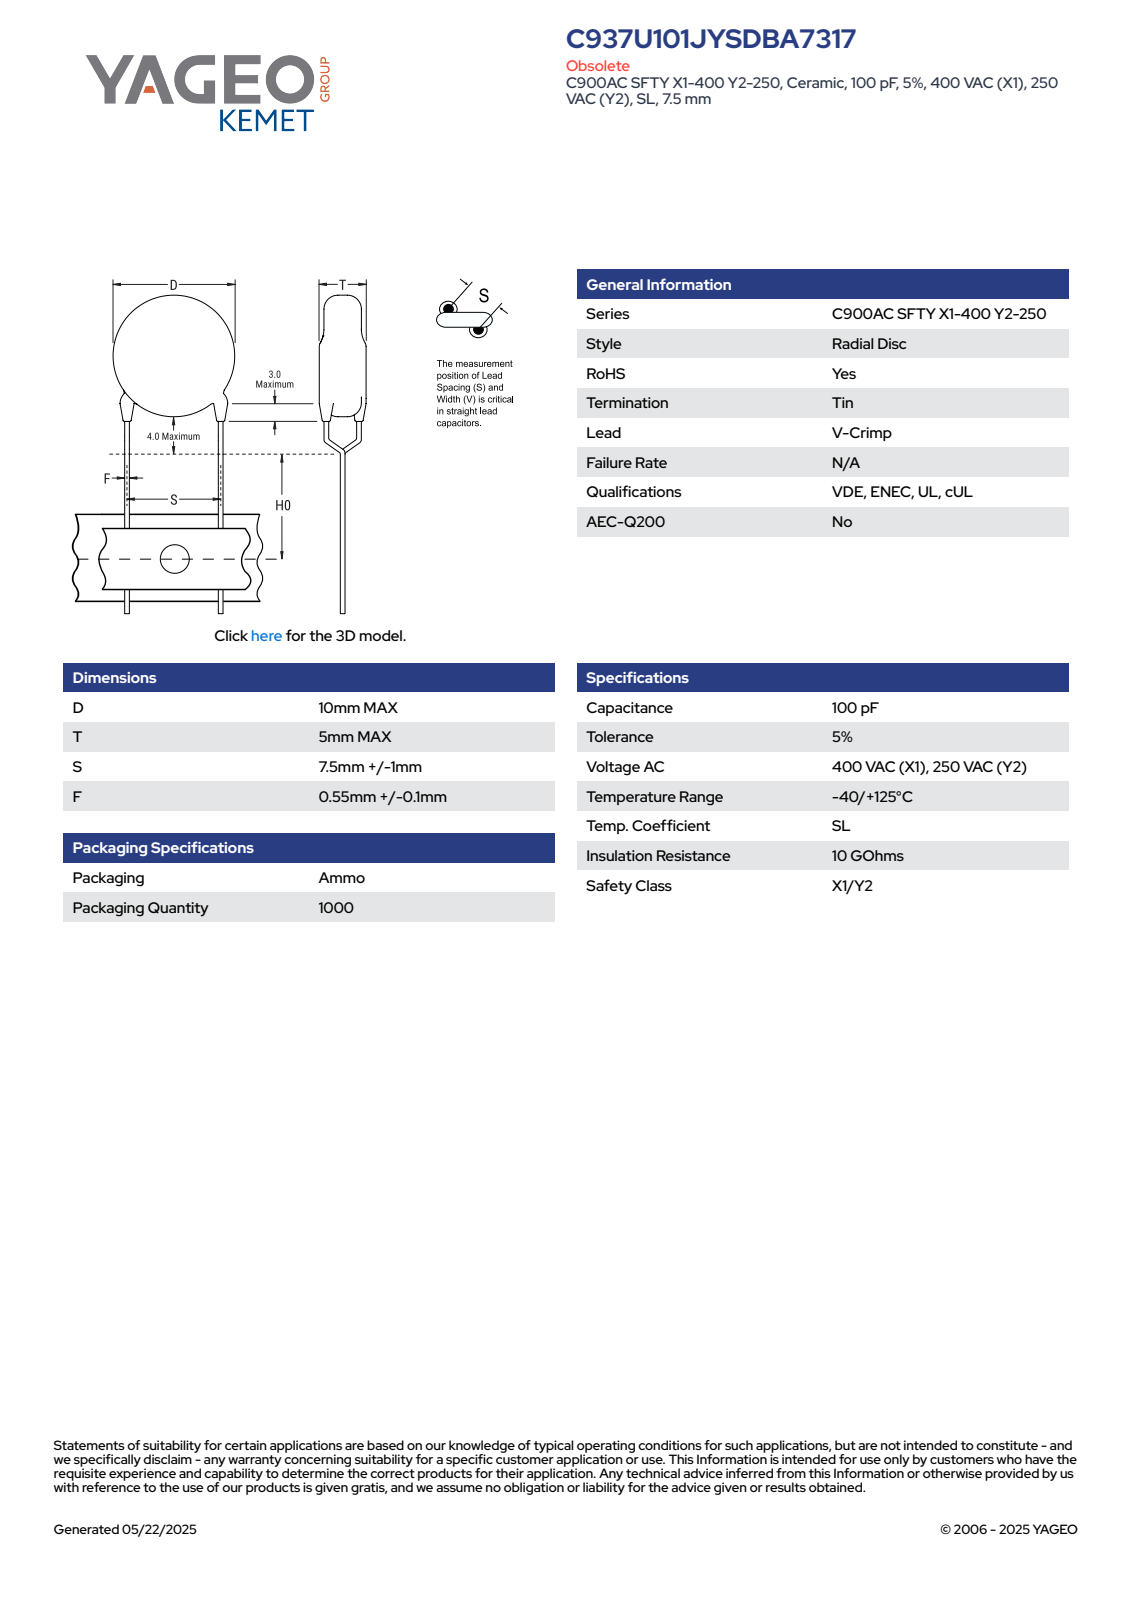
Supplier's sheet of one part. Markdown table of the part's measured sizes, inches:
| quantity | value |
| --- | --- |
| part name | CCD_VCC900_D10T5S7.5LL20F0.65 |
| STEP written by | SolidWorks 2014 (AUTOMOTIVE_DESIGN) |
| units | inches |
| bodies | 5 solids, 93 faces (65 planar, 16 cylindrical, 12 other) |
| overall size | 1.331 × 0.394 × 0.197 |
| volume | 0.024 in³ |
| surface area | 0.626 in² |
| round bosses / shafts (diameter × count) | 0.026 × 6, 0.394 × 1 |
| main face-to-face distances | 0.197, 0.902, 0.051, 1.159, 0.258, 1.108, 0.207, 0.013, 0.041, 0.106 |
